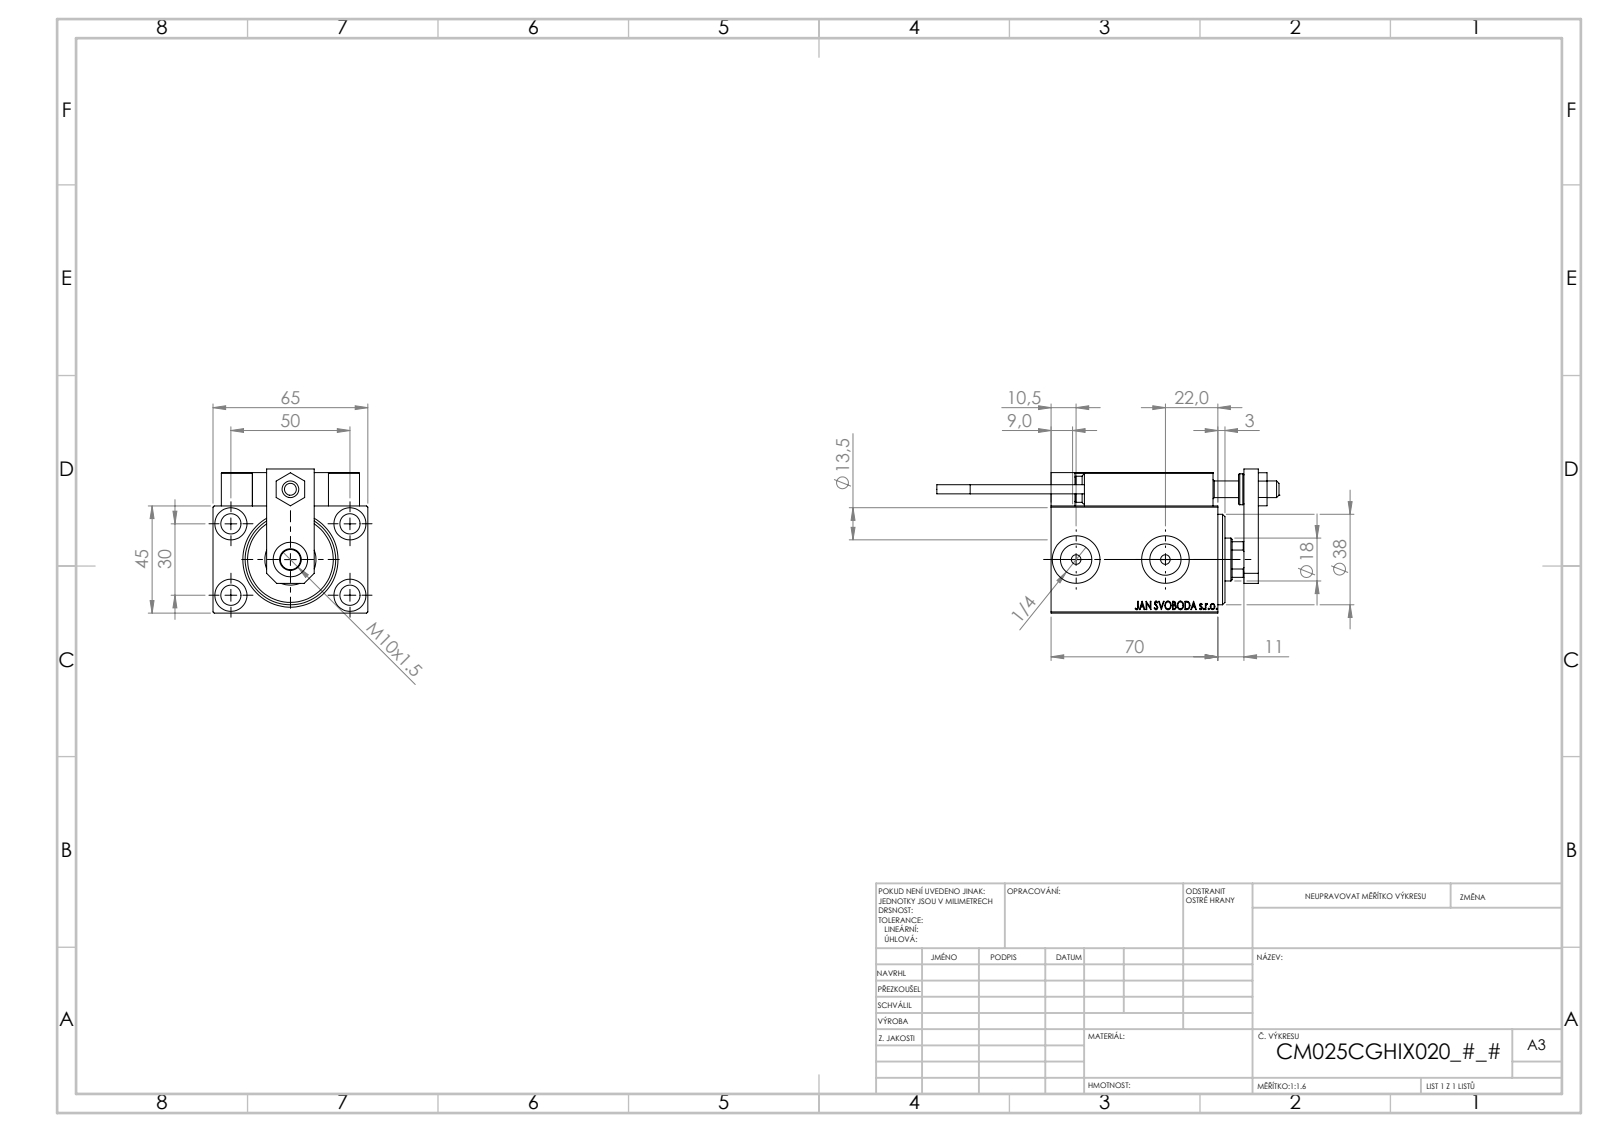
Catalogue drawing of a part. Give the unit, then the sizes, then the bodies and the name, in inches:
Units: inches
Overall size (bounding box): 5.657 × 2.559 × 2.382
Round holes (diameter × count): ⌀0.157 ×6, ⌀0.315 ×5, ⌀0.335 ×5, ⌀0.126 ×4, ⌀0.531 ×4, ⌀0.197 ×2, ⌀0.518 ×2, ⌀0.787 ×2, ⌀0.276 ×1, ⌀0.571 ×1, ⌀0.709 ×1, ⌀0.846 ×1
Round bosses / shafts (diameter × count): ⌀0.197 ×2, ⌀0.15 ×2, ⌀0.512 ×1, ⌀0.433 ×1
Partial cylindrical surfaces — rounded edges, fillets, slot ends (radius × count): R0.012 ×30, R0.118 ×2, R0.335 ×1
Main face-to-face distances: 1.772, 2.323, 2.559, 0.551, 0.236, 0.118, 0.276, 0.512, 0.138, 0.197
Hole centre spacings: 1.148, 0.448, 0.787, 0.87, 1.138, 1.165, 1.169, 1.181
Volume: 13.62 in³ · Surface area: 109.7 in²
Bodies: 23 solids, 1282 faces (560 planar, 188 cylindrical, 534 other)
Part name (STEP PRODUCT): ALLEN BOLT D5; ALLEN BOLT D8; KONCOVKA; ZARAZKA (+8 more)
STEP written by: SolidWorks 2019 (CONFIG_CONTROL_DESIGN)
